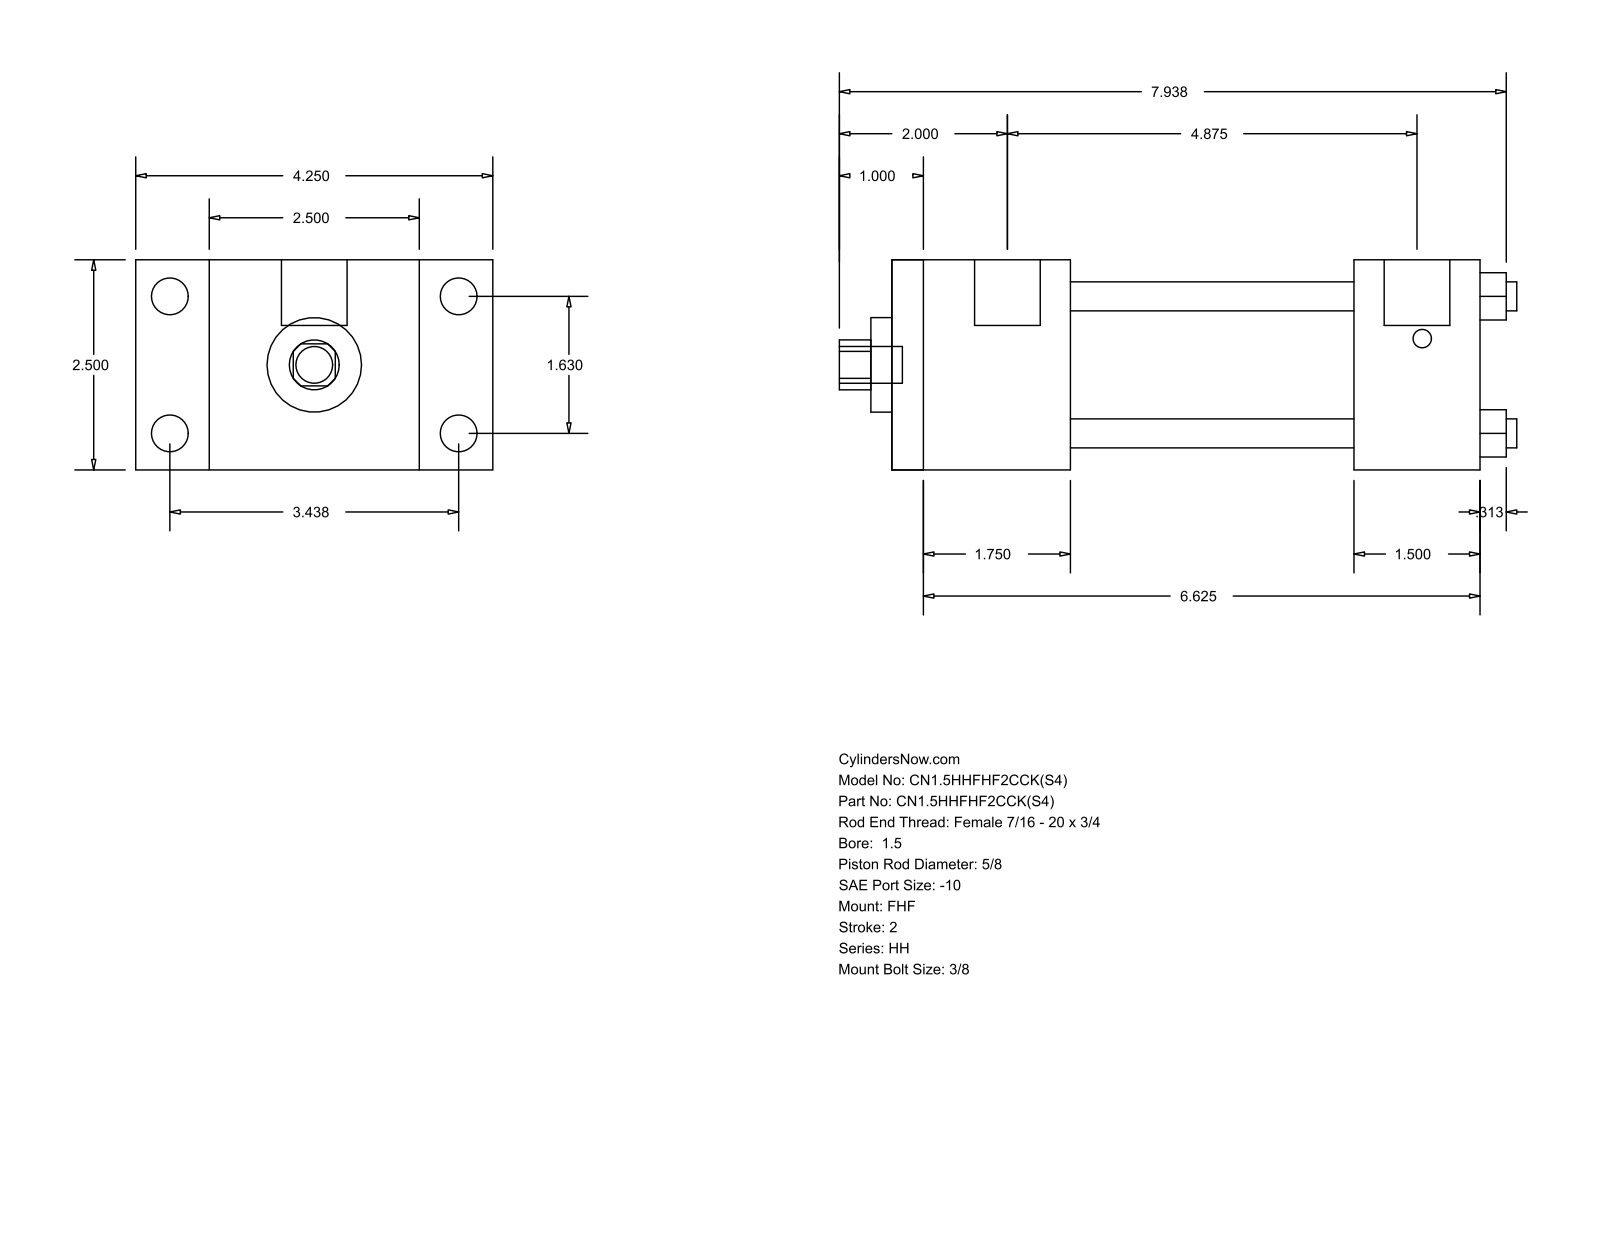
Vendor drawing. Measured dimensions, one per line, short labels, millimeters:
name: HH_FHF__0150_0.625
written by: GSSL Pune (CONFIG_CONTROL_DESIGN)
unit: mm
bodies: 0 solids, 88 faces (60 planar, 28 cylindrical, 0 other)
size: 204.79 × 107.95 × 63.5
holes: 4× ⌀8.76, 1× ⌀15.88, 1× ⌀28.57, 1× ⌀44.45
bosses: 4× ⌀11.13, 4× ⌀5.56, 2× ⌀19.84, 1× ⌀11.11
rounds: 1× R7.54
face distances: 63.5, 22.23, 85.73, 53.97, 107.96, 177.8, 123.83, 85.72, 139.69, 38.11
hole spacings: 29.27, 41.4, 58.55
